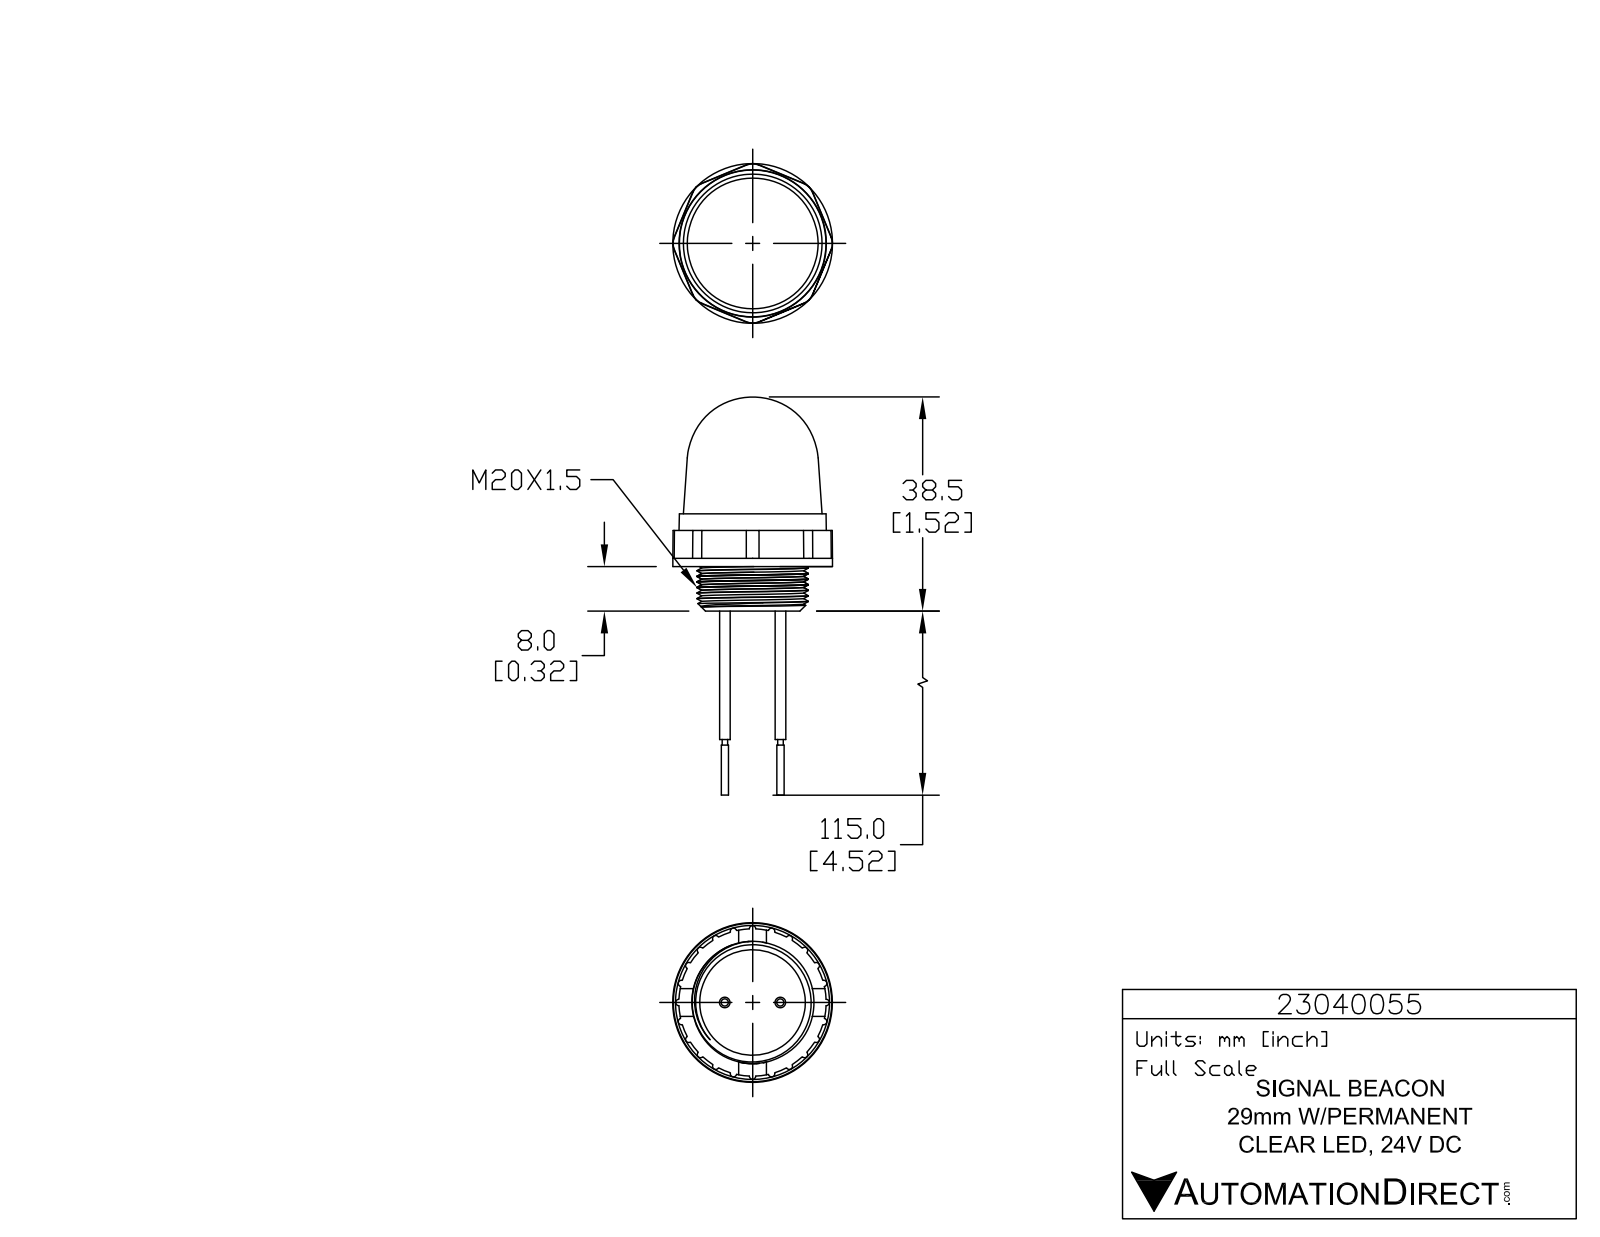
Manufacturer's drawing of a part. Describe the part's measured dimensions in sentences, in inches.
The part is named "23040055". Its 3-D file was written by "SolidWorks 2017 (AUTOMOTIVE_DESIGN)". It is 1 solid with 844 faces: 551 planar, 203 cylindrical and 90 other. Overall it measures 2.82 by 1.131 by 1.131 inches. Its volume is 0.978 cubic inches and its surface area 8.158 square inches. Round holes: 3 of diameter 0.02, 1 of diameter 0.807. Round bosses or shafts: 3 of diameter 0.113, 3 of diameter 0.028, 2 of diameter 0.075, 2 of diameter 0.051, 2 of diameter 0.039, 1 of diameter 1.131, 1 of diameter 1.122, 1 of diameter 0.894. Partial cylindrical surfaces (rounded edges, fillets, slot ends): 8 of radius 0.118, 6 of radius 0.004, 6 of radius 0.004, 6 of radius 0.004, 6 of radius 0.065, 3 of radius 0.005, 3 of radius 0.007, 3 of radius 0.008. The main face-to-face distances are 0.276, 0.374, 0.039, 0.315, 0.65, 0.638, 0.362, 0.689, 0.413, 0.051.
